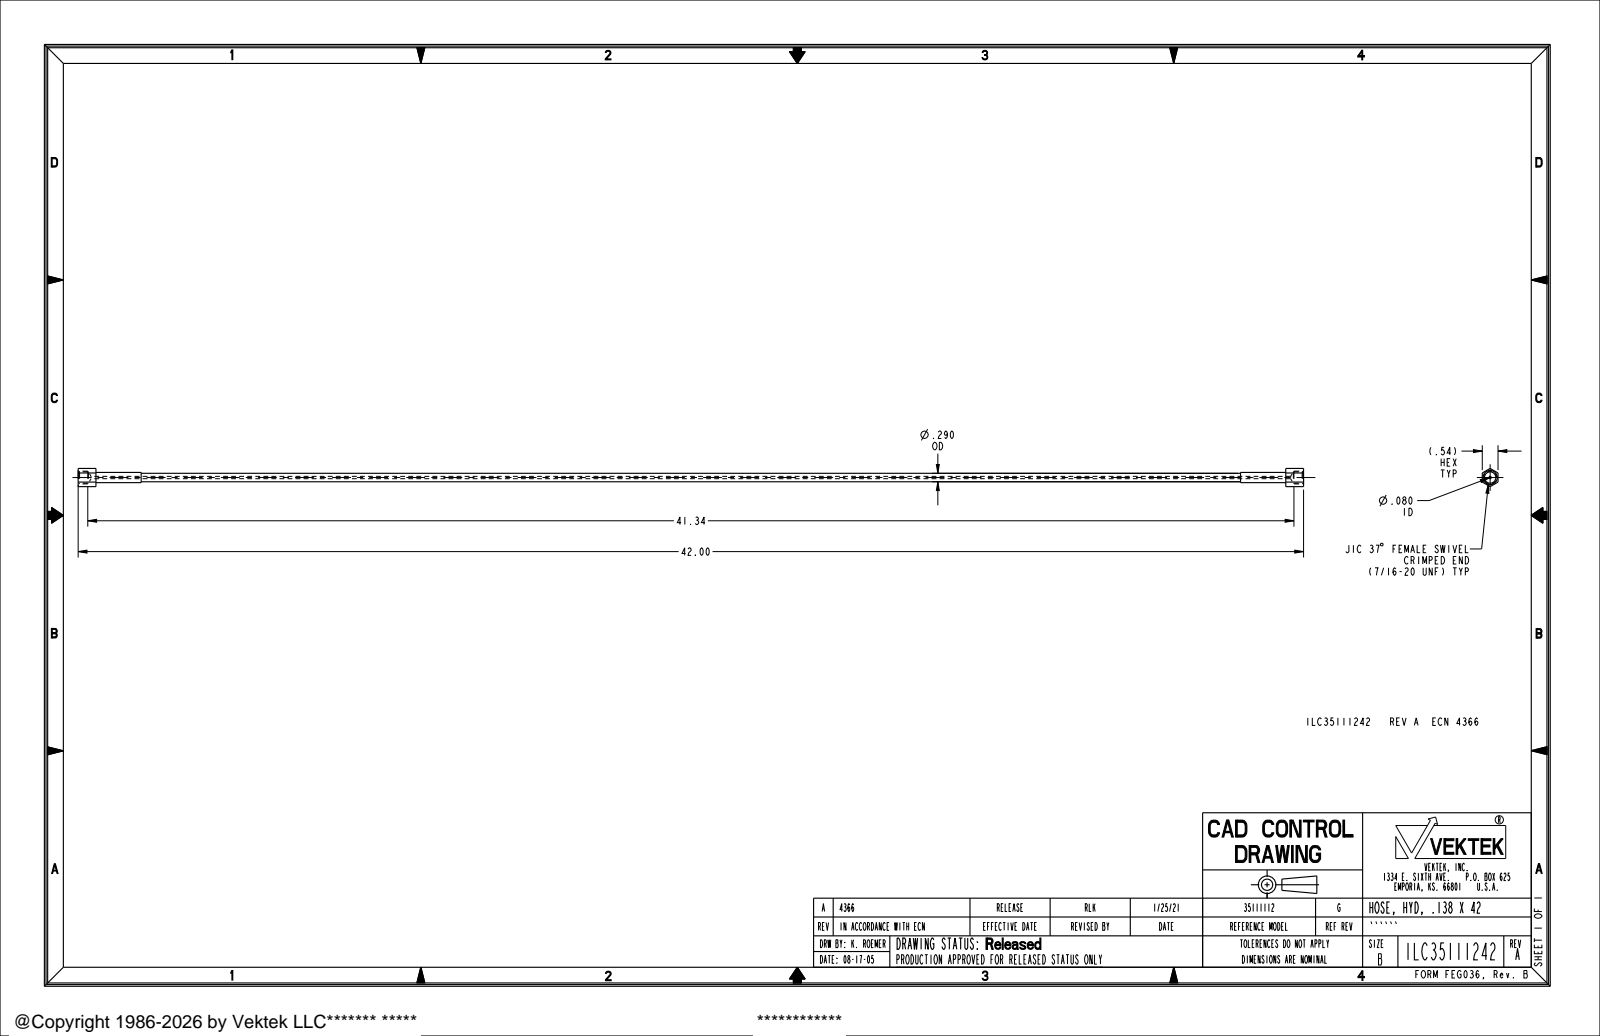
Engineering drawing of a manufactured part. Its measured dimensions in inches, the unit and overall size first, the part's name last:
Units: inches
Overall size (bounding box): 42 × 0.624 × 0.54
Round holes (diameter × count): ⌀0.08 ×1, ⌀0.391 ×1, ⌀0.437 ×1
Round bosses / shafts (diameter × count): ⌀0.35 ×1, ⌀0.29 ×1
Main face-to-face distances: 0.54, 40.78, 0.61, 41.39, 42, 0.33, 41.67, 0.28, 41.06, 2.16
Volume: 2.792 in³ · Surface area: 52.95 in²
Bodies: 1 solid, 44 faces (20 planar, 16 cylindrical, 8 other)
Part name (STEP PRODUCT): ILC35111242
STEP written by: PRO/ENGINEER BY PARAMETRIC TECHNOLOGY CORPORATION, 2017170 (AUTOMOTIVE_DESIGN)
